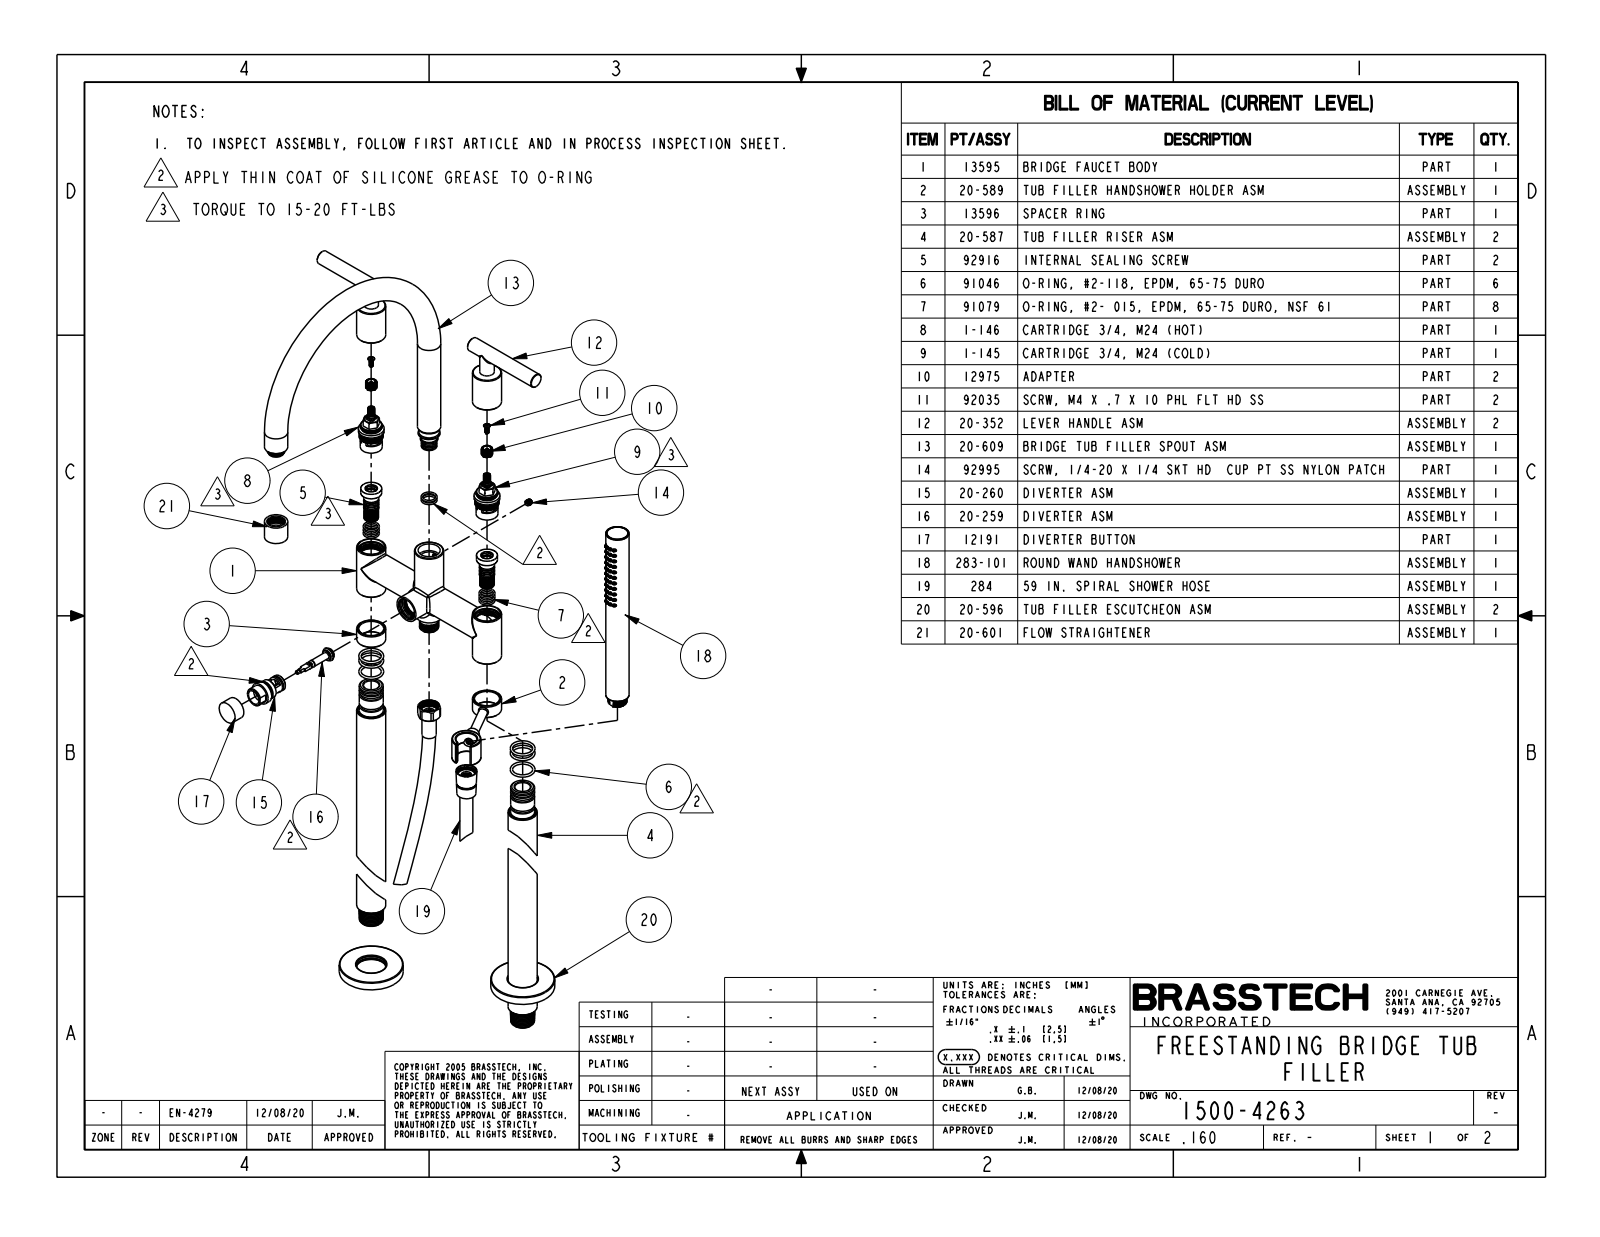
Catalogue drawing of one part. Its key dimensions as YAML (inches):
part_name: "1500-4263"
step_written_by: "CREO PARAMETRIC BY PTC INC, 2019352 (CONFIG_CONTROL_DESIGN)"
units: inches
bodies: {solids: 4, faces: 1414, planar: 213, cylindrical: 452, other: 749}
overall_size: [41.923, 15.125, 10.875]
volume: 130.8
surface_area: 523.3
round_holes:
  - {diameter: 0.14, count: 44}
  - {diameter: 0.118, count: 1}
  - {diameter: 0.606, count: 1}
  - {diameter: 0.691, count: 1}
  - {diameter: 0.886, count: 1}
  - {diameter: 0.94, count: 1}
round_bosses_or_shafts:
  - {diameter: 1.25, count: 5}
  - {diameter: 1, count: 3}
  - {diameter: 0.625, count: 3}
  - {diameter: 0.56, count: 3}
  - {diameter: 2.75, count: 2}
  - {diameter: 1.15, count: 2}
  - {diameter: 0.965, count: 1}
  - {diameter: 0.91, count: 1}
partial_cylinders:
  - {radius: 0.03, count: 6}
  - {radius: 0.1, count: 4}
  - {radius: 0.3, count: 1}
  - {radius: 0.34, count: 1}
  - {radius: 0.365, count: 1}
  - {radius: 0.41, count: 1}
  - {radius: 0.45, count: 1}
  - {radius: 0.494, count: 1}
face_to_face_distances: [0.38, 32.415, 32.035, 2.367, 32.458, 32.078, 0.043, 37.31, 36.93, 4.895]
hole_center_spacings: [0.604, 0.336, 0.17, 0.887, 1.172, 0.58, 0.672, 0.29]
